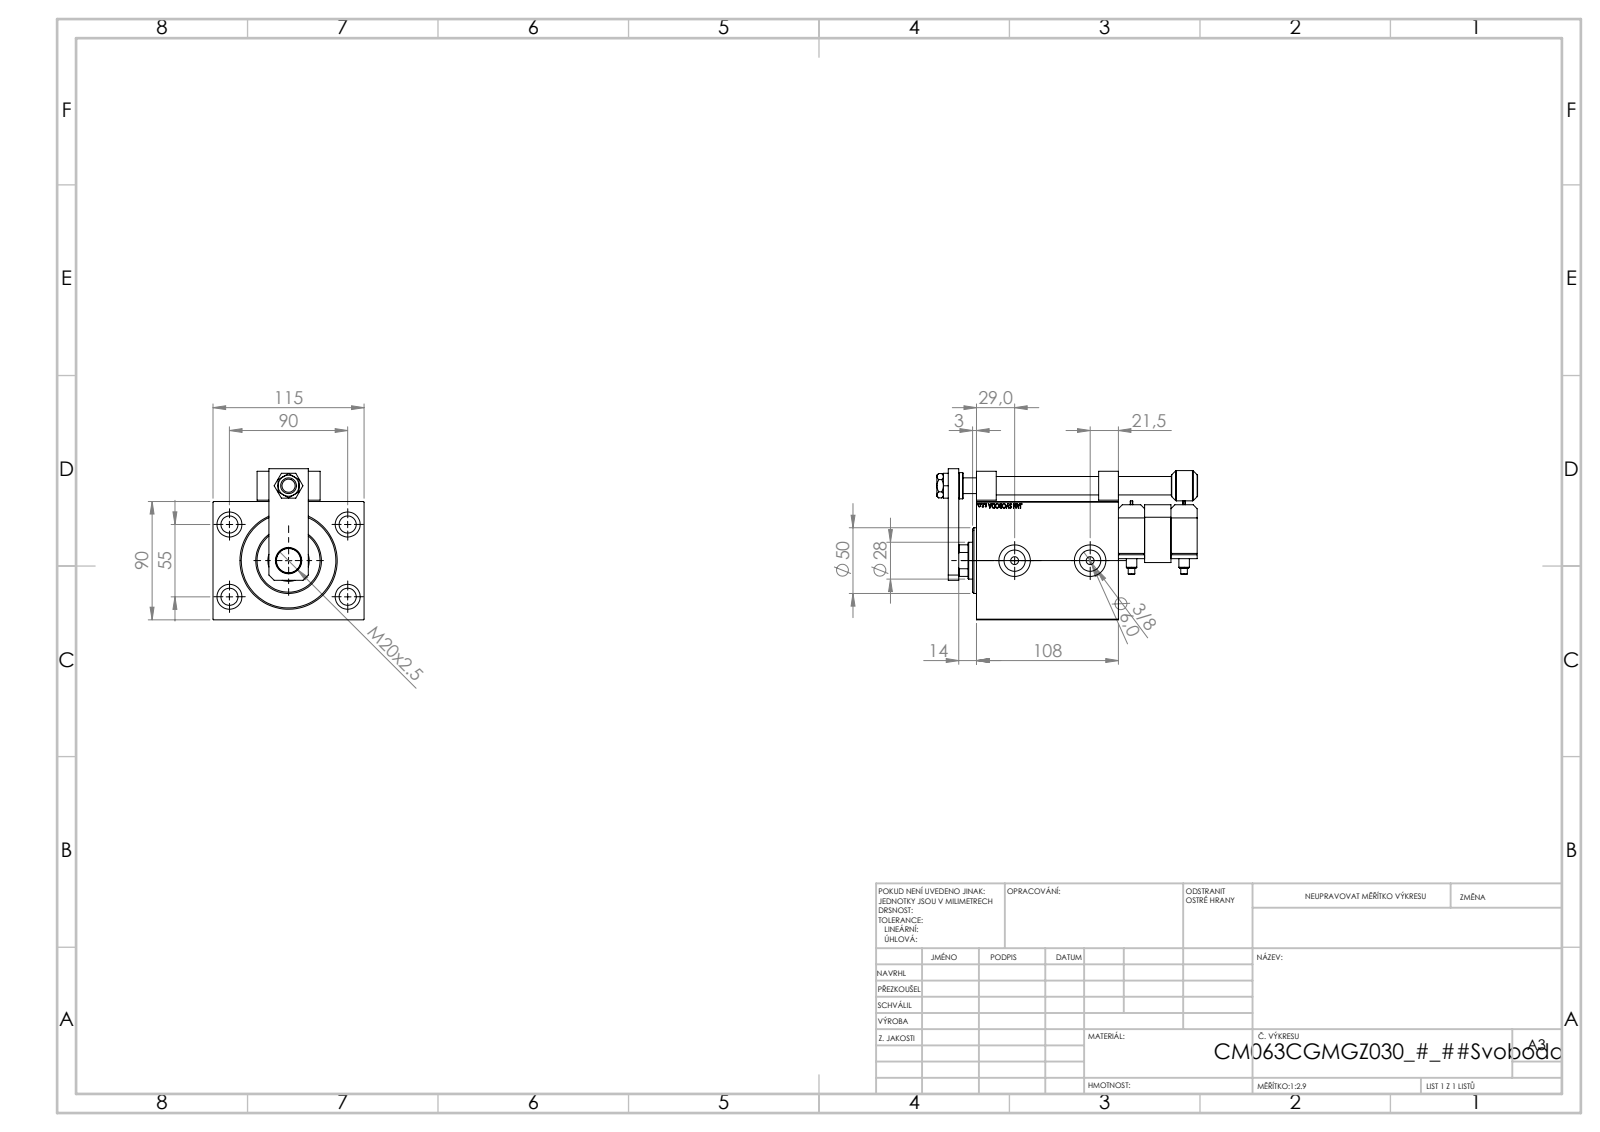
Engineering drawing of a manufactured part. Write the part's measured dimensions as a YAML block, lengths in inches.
part_name: "MIDDLE; SWITCH_P_FRONT_BACK; V450CM_C_VCP; NUT_D16 (+7 more)"
step_written_by: "SolidWorks 2019 (CONFIG_CONTROL_DESIGN)"
units: inches
bodies: {solids: 14, faces: 1118, planar: 525, cylindrical: 128, other: 465}
overall_size: [7.815, 4.528, 4.528]
volume: 69.87
surface_area: 292
round_holes:
  - {diameter: 0.512, count: 5}
  - {diameter: 0.157, count: 4}
  - {diameter: 0.315, count: 4}
  - {diameter: 0.748, count: 4}
  - {diameter: 0.236, count: 2}
  - {diameter: 0.637, count: 2}
  - {diameter: 0.945, count: 2}
  - {diameter: 0.472, count: 1}
  - {diameter: 0.551, count: 1}
  - {diameter: 0.728, count: 1}
  - {diameter: 0.787, count: 1}
  - {diameter: 1.102, count: 1}
round_bosses_or_shafts:
  - {diameter: 0.787, count: 3}
  - {diameter: 0.63, count: 2}
  - {diameter: 0.551, count: 2}
  - {diameter: 0.315, count: 2}
  - {diameter: 0.236, count: 2}
  - {diameter: 0.198, count: 2}
  - {diameter: 1.969, count: 1}
  - {diameter: 0.906, count: 1}
partial_cylinders:
  - {radius: 0.118, count: 1}
  - {radius: 0.531, count: 1}
face_to_face_distances: [3.543, 4.528, 0.787, 4.252, 0.689, 1.476, 3.563, 1.575, 0.531, 3.051]
hole_center_spacings: [2.076, 0.787, 2.119, 2.165, 3.543, 3.661, 3.745, 3.769]
